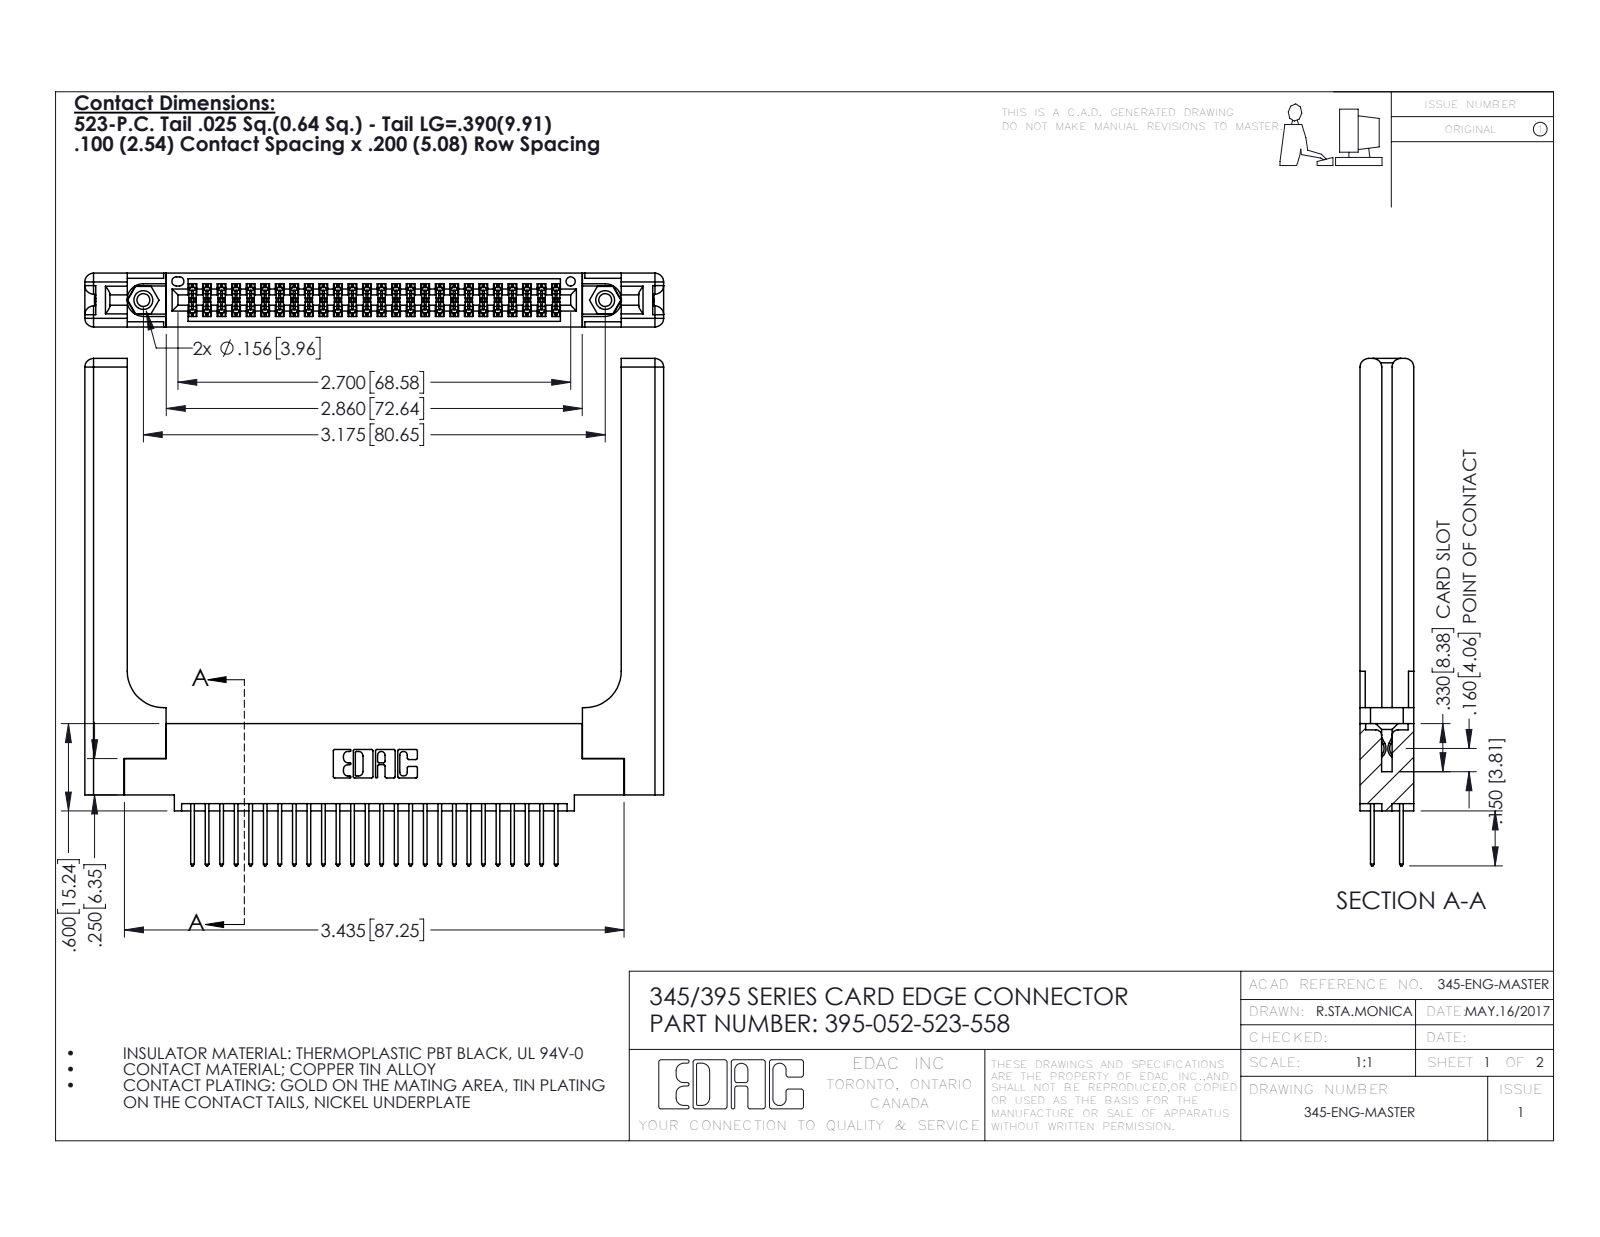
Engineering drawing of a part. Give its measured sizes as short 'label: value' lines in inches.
name: 395-052-523-558; 345-250-001_345-250-001-102; 345-292-001_345-293-123; 345 Part_0.110 Offset - 0.156 Dia-TH (+1 more)
written by: SolidWorks 2016 (CONFIG_CONTROL_DESIGN)
unit: in
bodies: 57 solids, 2986 faces (1948 planar, 978 cylindrical, 60 other)
size: 3.979 × 3.487 × 0.37
volume: 1.109 in³; area: 30.48 in²
holes: 2× ⌀0.089, 2× ⌀0.125, 2× ⌀0.156, 1× ⌀0.064
bosses: 2× ⌀0.155
rounds: 78× R0.006, 52× R0.01, 22× R0.01, 16× R0.06, 6× R0.007, 6× R0.031, 3× R0.026, 2× R0.014
face distances: 0.072, 0.37, 0.298, 0.098, 0.272, 0.025, 0.2, 0.225, 0.148, 0.15
hole spacings: 0.27, 2.94, 3.175
